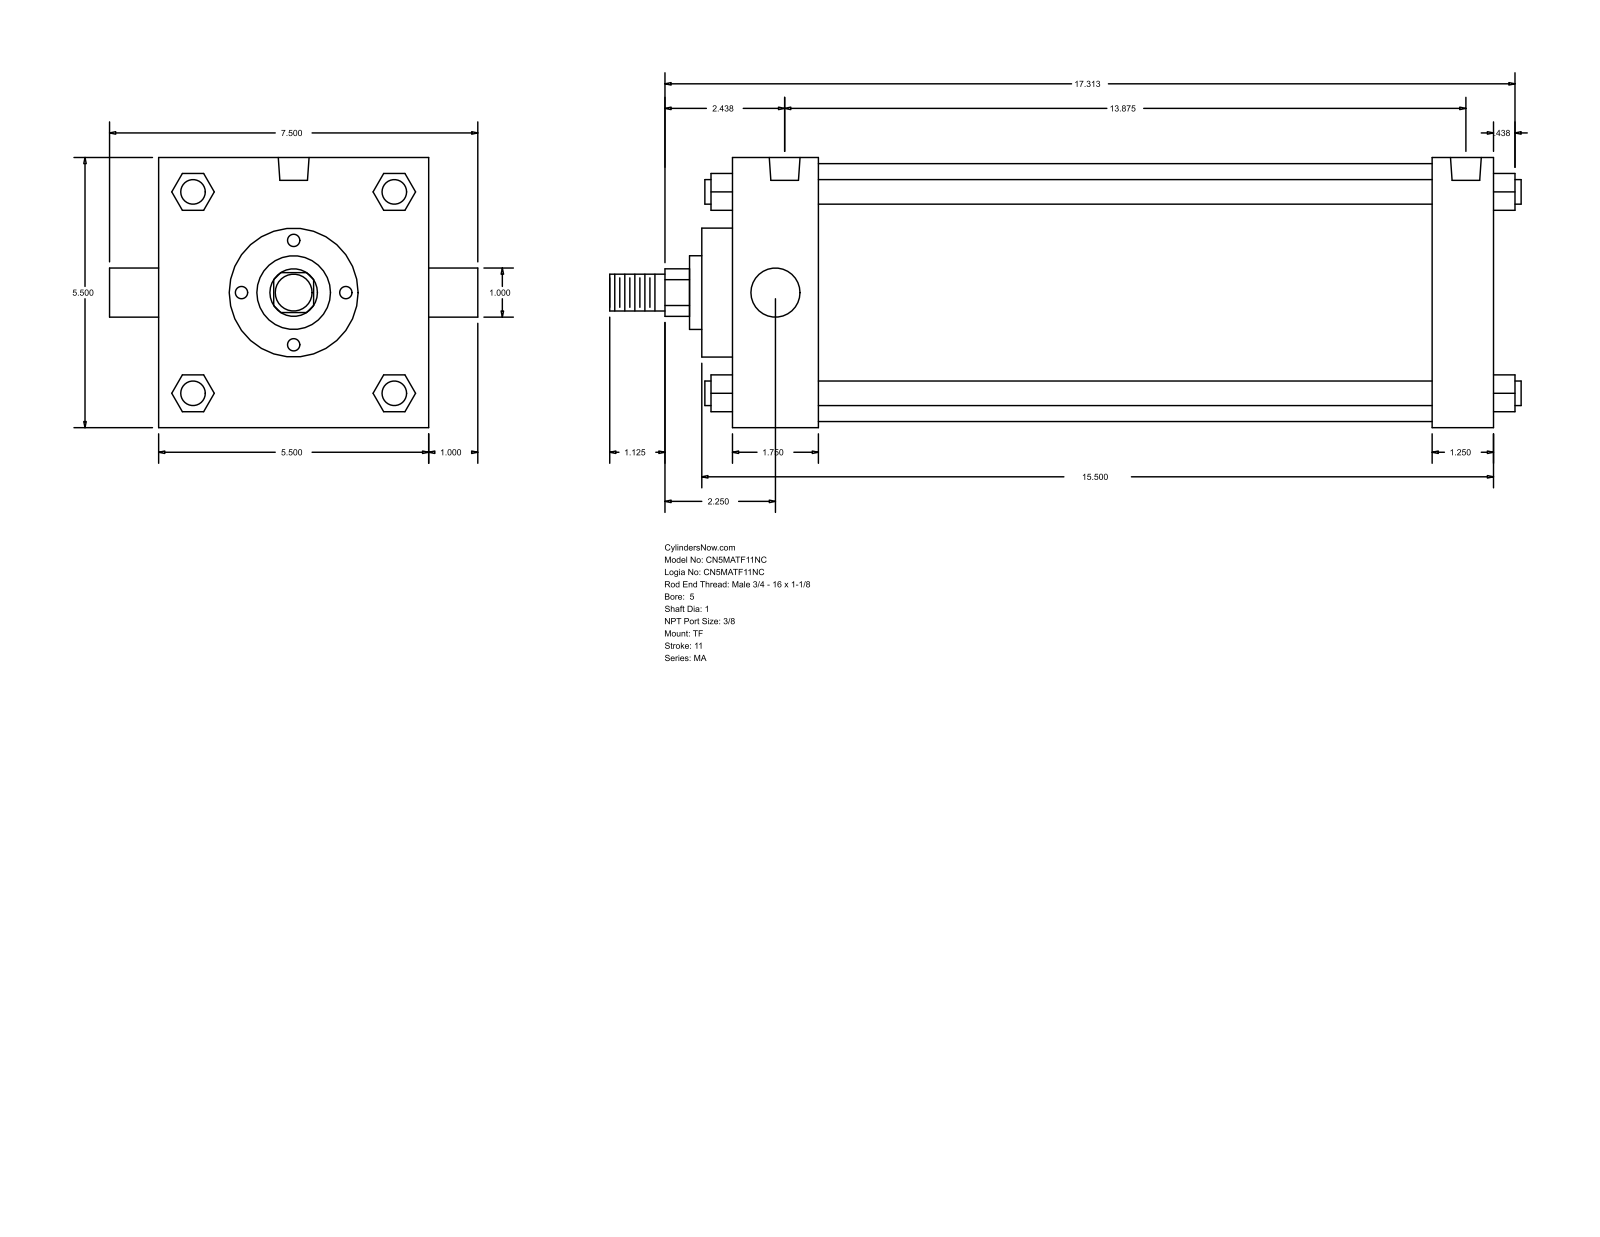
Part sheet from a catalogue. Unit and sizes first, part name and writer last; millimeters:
Units: millimetres
Overall size (bounding box): 471.49 × 190.5 × 139.7
Round holes (diameter × count): ⌀11.11 ×3, ⌀15.93 ×2
Round bosses / shafts (diameter × count): ⌀12.7 ×4, ⌀25.4 ×2, ⌀133.35 ×1, ⌀66.67 ×1, ⌀38.1 ×1, ⌀19.05 ×1
Partial cylindrical surfaces — rounded edges, fillets, slot ends (radius × count): R12.29 ×1
Main face-to-face distances: 139.7, 393.7, 361.96, 31.74, 44.46, 317.5, 349.24, 15.87, 60.33, 377.83
Hole centre spacings: 4.76, 4.77, 342.9, 347.66, 347.67, 352.43
Bodies: 0 solids, 122 faces (93 planar, 29 cylindrical, 0 other)
Part name (STEP PRODUCT): MA_TF__0500_1
STEP written by: GSSL Pune (CONFIG_CONTROL_DESIGN)
